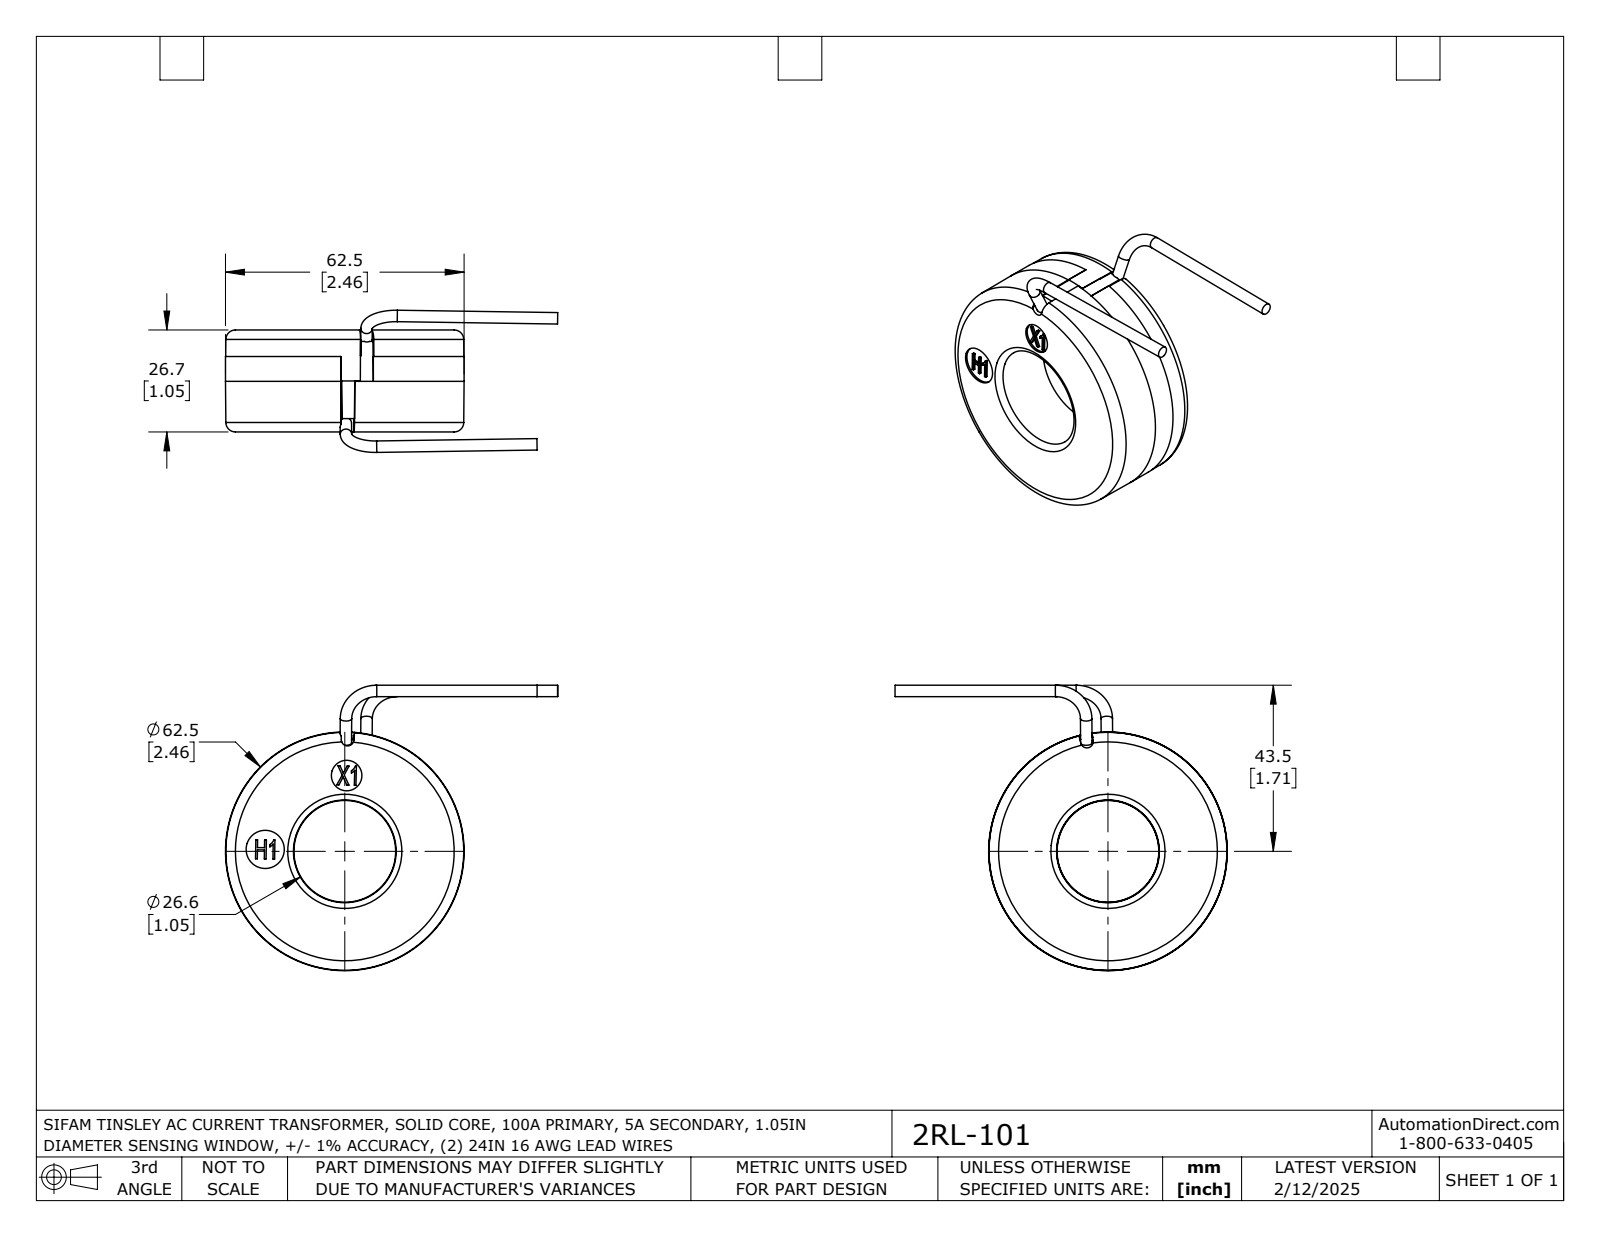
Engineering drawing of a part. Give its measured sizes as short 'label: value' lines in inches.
name: 2RL-101
written by: SolidWorks 2021 (AUTOMOTIVE_DESIGN)
unit: in
bodies: 1 solid, 129 faces (62 planar, 18 cylindrical, 49 other)
size: 3.439 × 2.943 × 1.463
volume: 4.069 in³; area: 20.81 in²
holes: 1× ⌀0.315, 1× ⌀0.394, 1× ⌀2.382
bosses: 4× ⌀0.118, 1× ⌀2.461
face distances: 1.051, 0.019, 1.032, 0.02, 1.031, 0.778, 0.758, 0.758, 0.274, 0.526
hole spacings: 0.782, 0.821, 1.133
